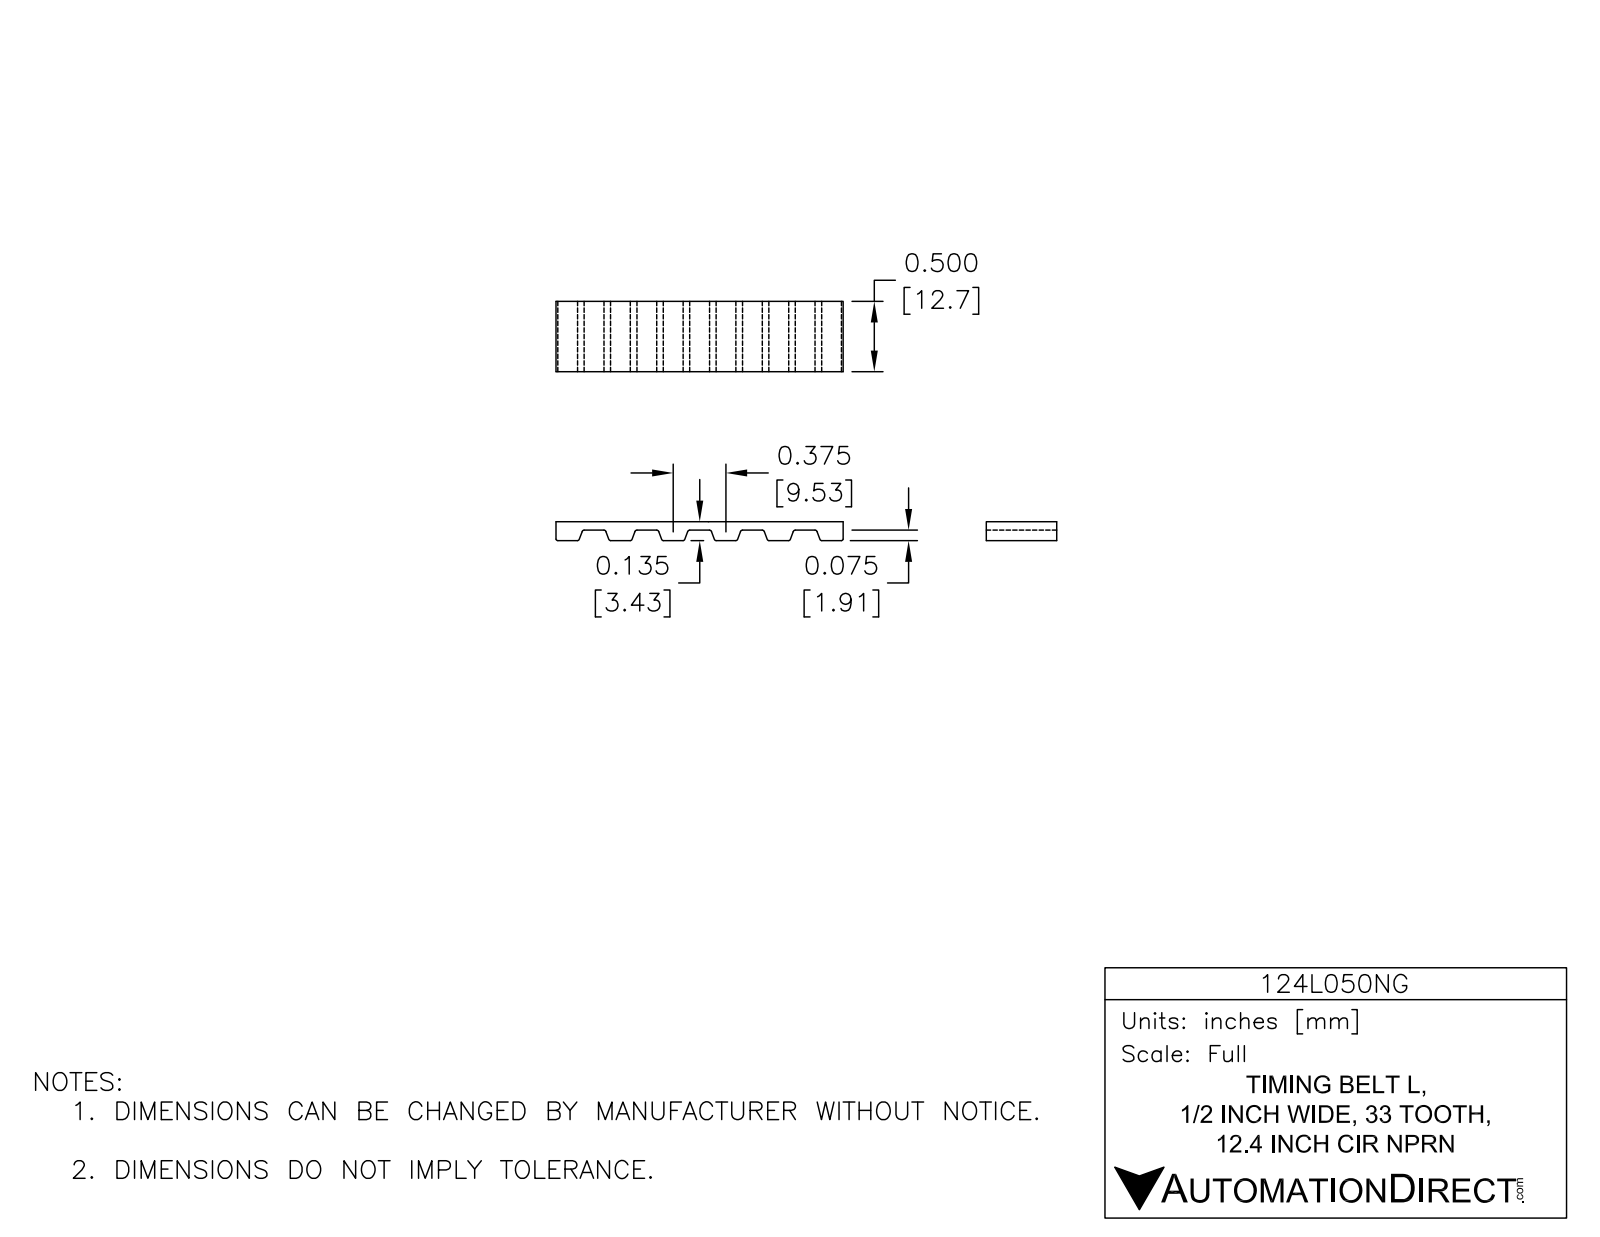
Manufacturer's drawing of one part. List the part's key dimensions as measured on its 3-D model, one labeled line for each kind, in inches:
Part name (STEP PRODUCT): 124L050NG
STEP written by: SolidWorks 2014 (AUTOMOTIVE_DESIGN)
Units: inches
Bodies: 1 solid, 290 faces (112 planar, 178 cylindrical, 0 other)
Overall size (bounding box): 4.475 × 3 × 0.5
Volume: 0.556 in³ · Surface area: 15.88 in²
Partial cylindrical surfaces — rounded edges, fillets, slot ends (radius × count): R0.02 ×132, R1.435 ×2, R1.5 ×2
Main face-to-face distances: 0.5, 3, 0.065, 2.935, 2.87, 0.14, 2.86, 0.075, 2.795, 0.341
